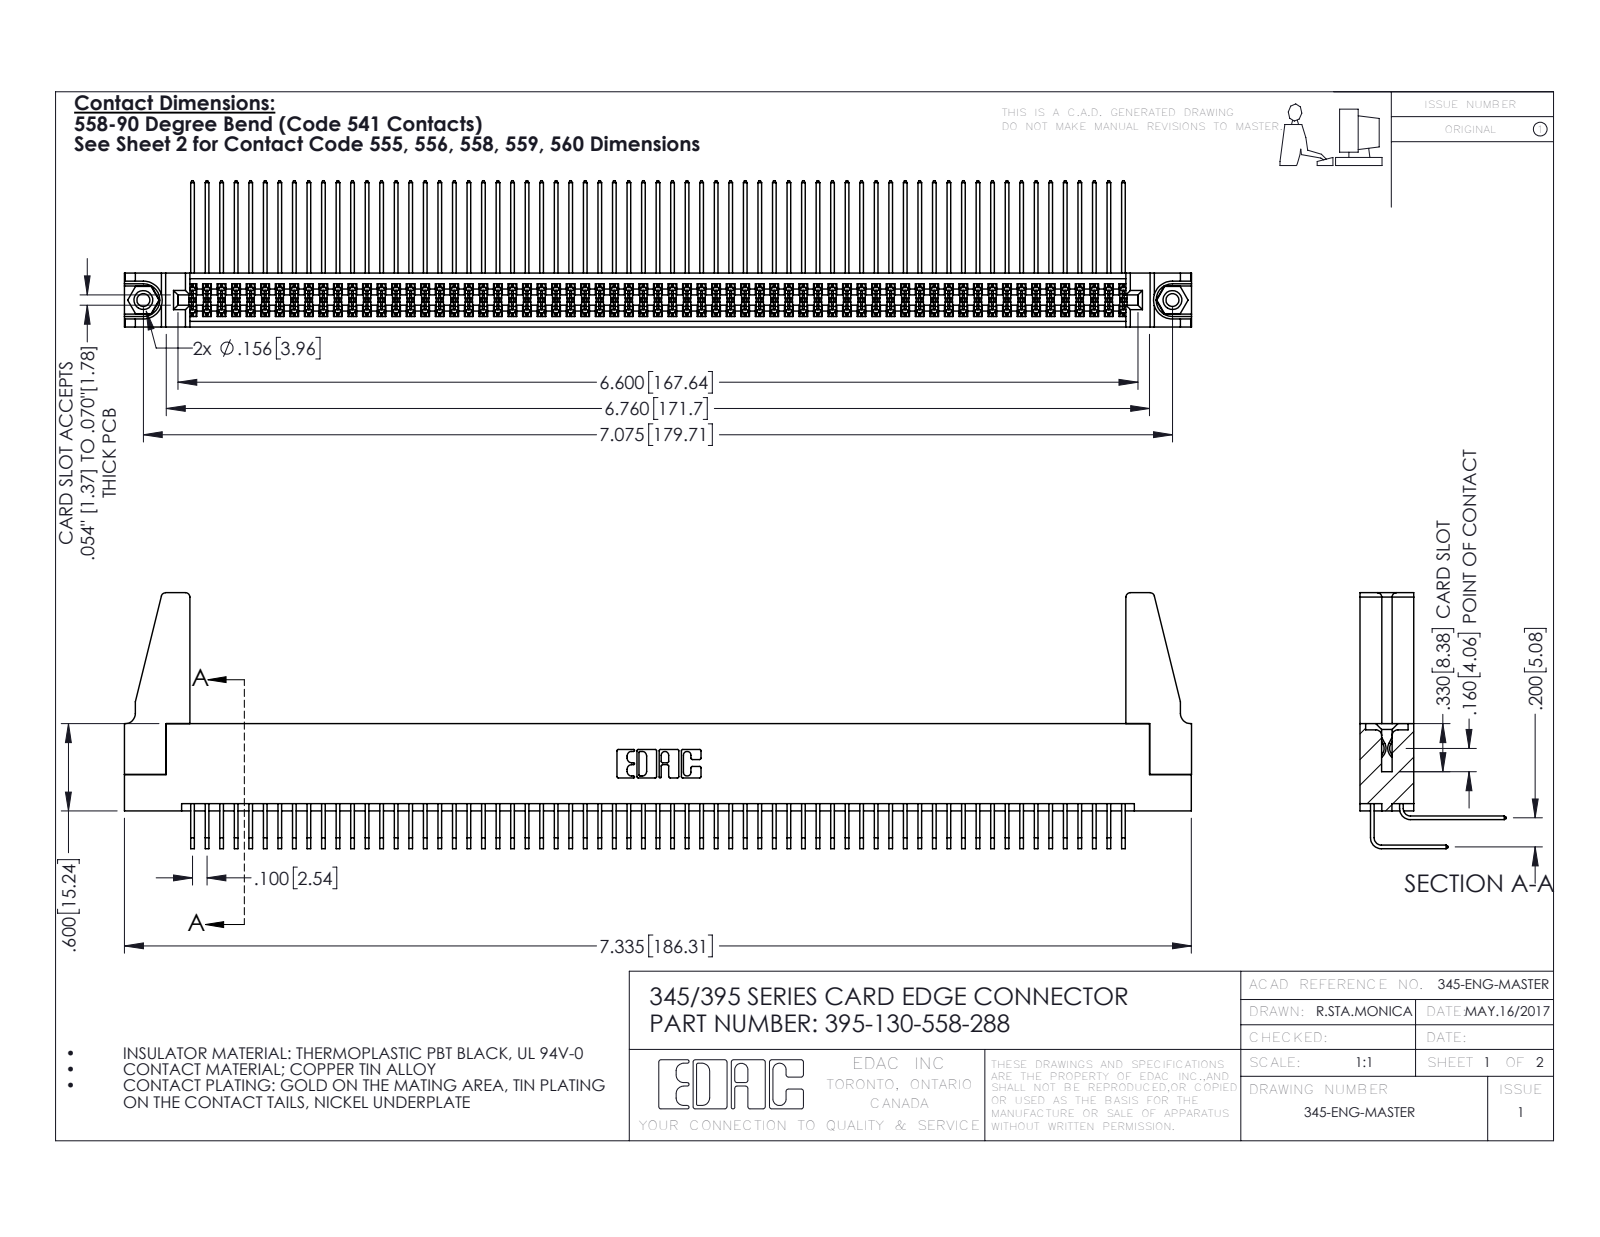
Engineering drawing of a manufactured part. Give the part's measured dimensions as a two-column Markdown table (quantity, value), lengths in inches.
| quantity | value |
| --- | --- |
| part name | 345-220-078_345-220-088; 345-292-001_558 Tail - 2; 345-250-001_345-250-001-102; 395-130-558-288 (+2 more) |
| STEP written by | SolidWorks 2016 (CONFIG_CONTROL_DESIGN) |
| units | inches |
| bodies | 135 solids, 7010 faces (4702 planar, 2292 cylindrical, 16 other) |
| overall size | 7.336 × 1.759 × 1.005 |
| volume | 1.362 in³ |
| surface area | 54.67 in² |
| round holes (diameter × count) | 0.089 × 2, 0.125 × 2, 0.156 × 2, 0.064 × 1 |
| round bosses / shafts (diameter × count) | 0.155 × 2 |
| partial cylindrical surfaces (radius × count) | 0.006 × 195, 0.01 × 22, 0.03 × 8, 0.007 × 6, 0.031 × 6, 0.026 × 3, 0.014 × 2, 0.019 × 2 |
| main face-to-face distances | 0.072, 0.298, 0.2, 0.37, 0.098, 0.272, 0.025, 0.225, 0.025, 0.285 |
| hole center spacings | 0.27, 6.839, 7.075 |
